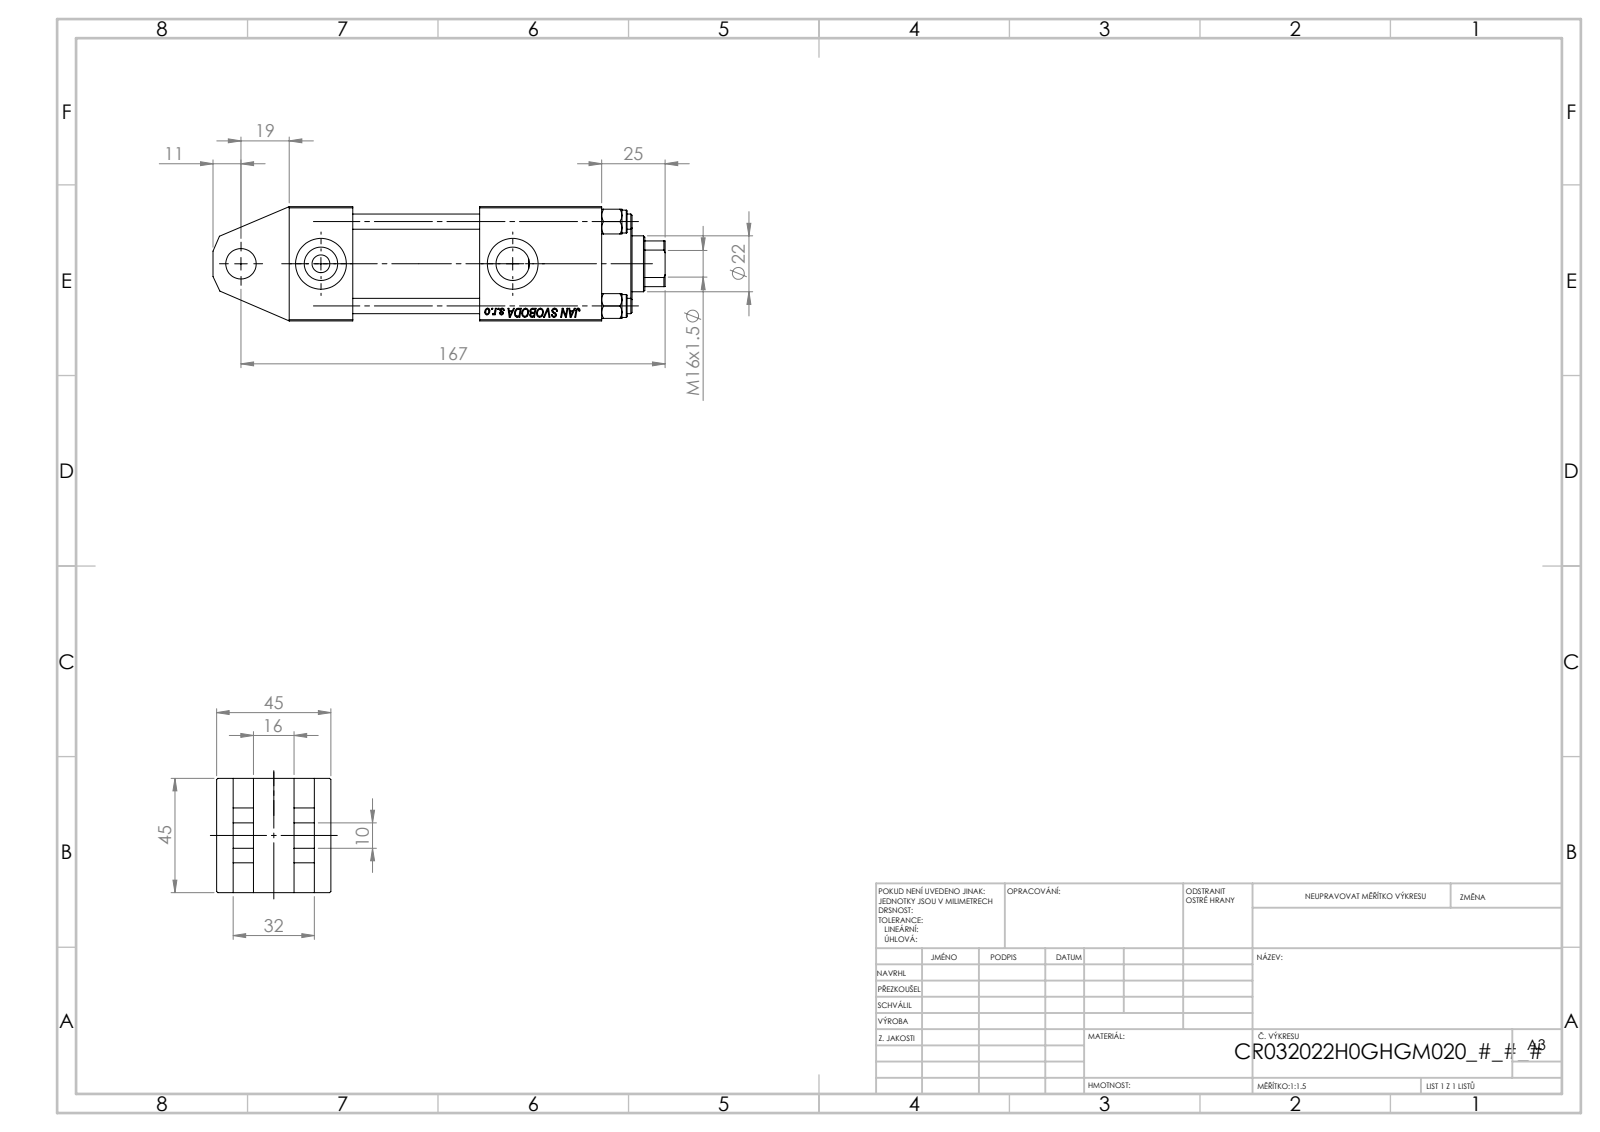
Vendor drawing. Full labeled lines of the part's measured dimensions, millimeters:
Part name (STEP PRODUCT): V215_VC_A; V215CR_H_Body; NUT_M5_H; V215CR_VCP_H (+1 more)
STEP written by: SolidWorks 2019 (CONFIG_CONTROL_DESIGN)
Units: millimetres
Bodies: 11 solids, 1136 faces (517 planar, 87 cylindrical, 532 other)
Overall size (bounding box): 178 × 45 × 45
Volume: 225 074 mm³ · Surface area: 78 504 mm²
Round holes (diameter × count): ⌀6 ×4, ⌀2.5 ×2, ⌀7 ×2, ⌀13.16 ×2, ⌀20 ×2, ⌀10.5 ×1, ⌀12 ×1, ⌀22 ×1, ⌀24 ×1, ⌀25 ×1, ⌀32 ×1, ⌀33 ×1
Round bosses / shafts (diameter × count): ⌀9 ×4, ⌀38 ×1, ⌀34 ×1
Partial cylindrical surfaces — rounded edges, fillets, slot ends (radius × count): R10.5 ×1
Main face-to-face distances: 45, 8, 38.5, 6.5, 14.5, 30.5, 24, 25, 123, 50
Hole centre spacings: 16.7, 23.48, 33.2, 35.47, 14.75, 46.95, 29.5, 31.5
